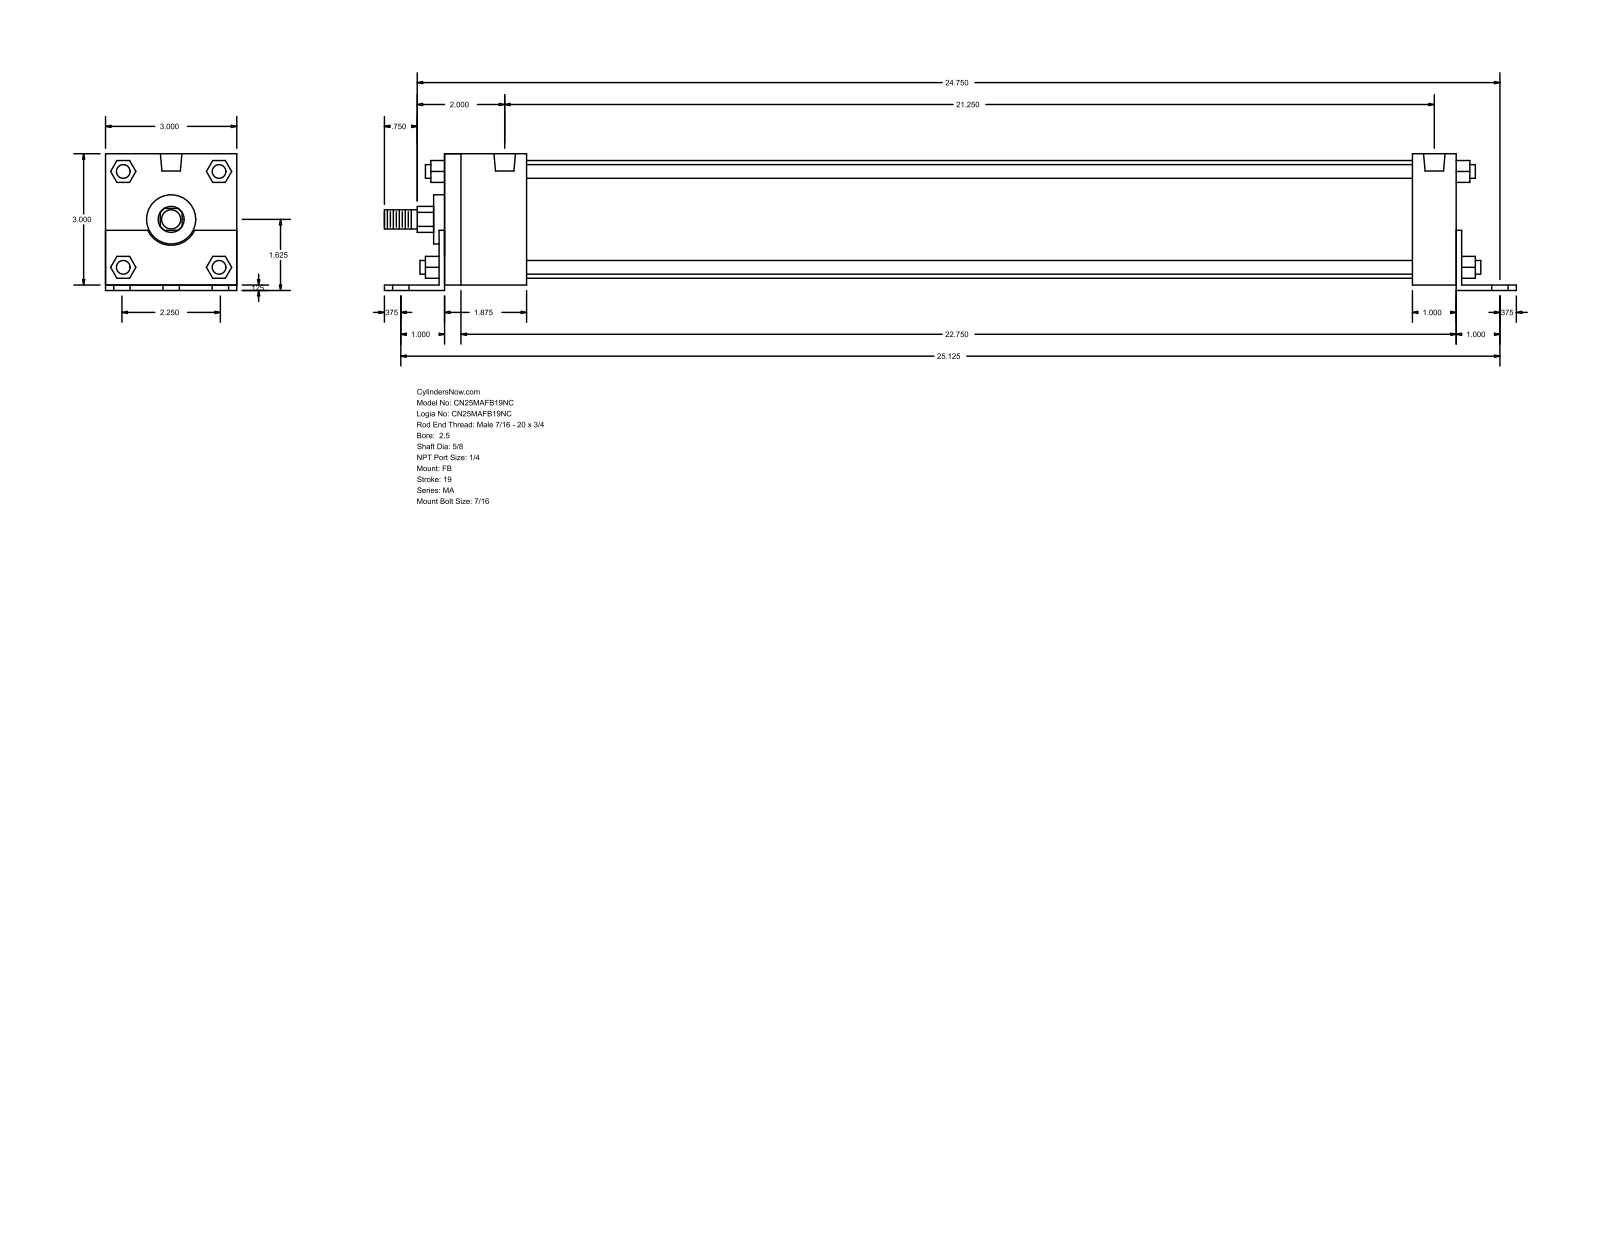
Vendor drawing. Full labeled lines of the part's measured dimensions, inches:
Part name (STEP PRODUCT): MA_FB__0250_0.625
STEP written by: GSSL Pune (CONFIG_CONTROL_DESIGN)
Units: inches
Bodies: 0 solids, 140 faces (105 planar, 35 cylindrical, 0 other)
Overall size (bounding box): 25.875 × 3.125 × 3
Round holes (diameter × count): ⌀0.437 ×6, ⌀0.313 ×4, ⌀0.492 ×2
Round bosses / shafts (diameter × count): ⌀0.313 ×4, ⌀2.69 ×1, ⌀1.125 ×1, ⌀0.625 ×1, ⌀0.437 ×1
Partial cylindrical surfaces — rounded edges, fillets, slot ends (radius × count): R0.297 ×1, R0.593 ×1
Main face-to-face distances: 3, 0.125, 3.125, 23.125, 23.375, 0.125, 23.25, 1.875, 1, 23.25
Hole centre spacings: 1.125, 25.15, 25.125, 1.875, 2.25, 2.628, 21.25, 22.778
